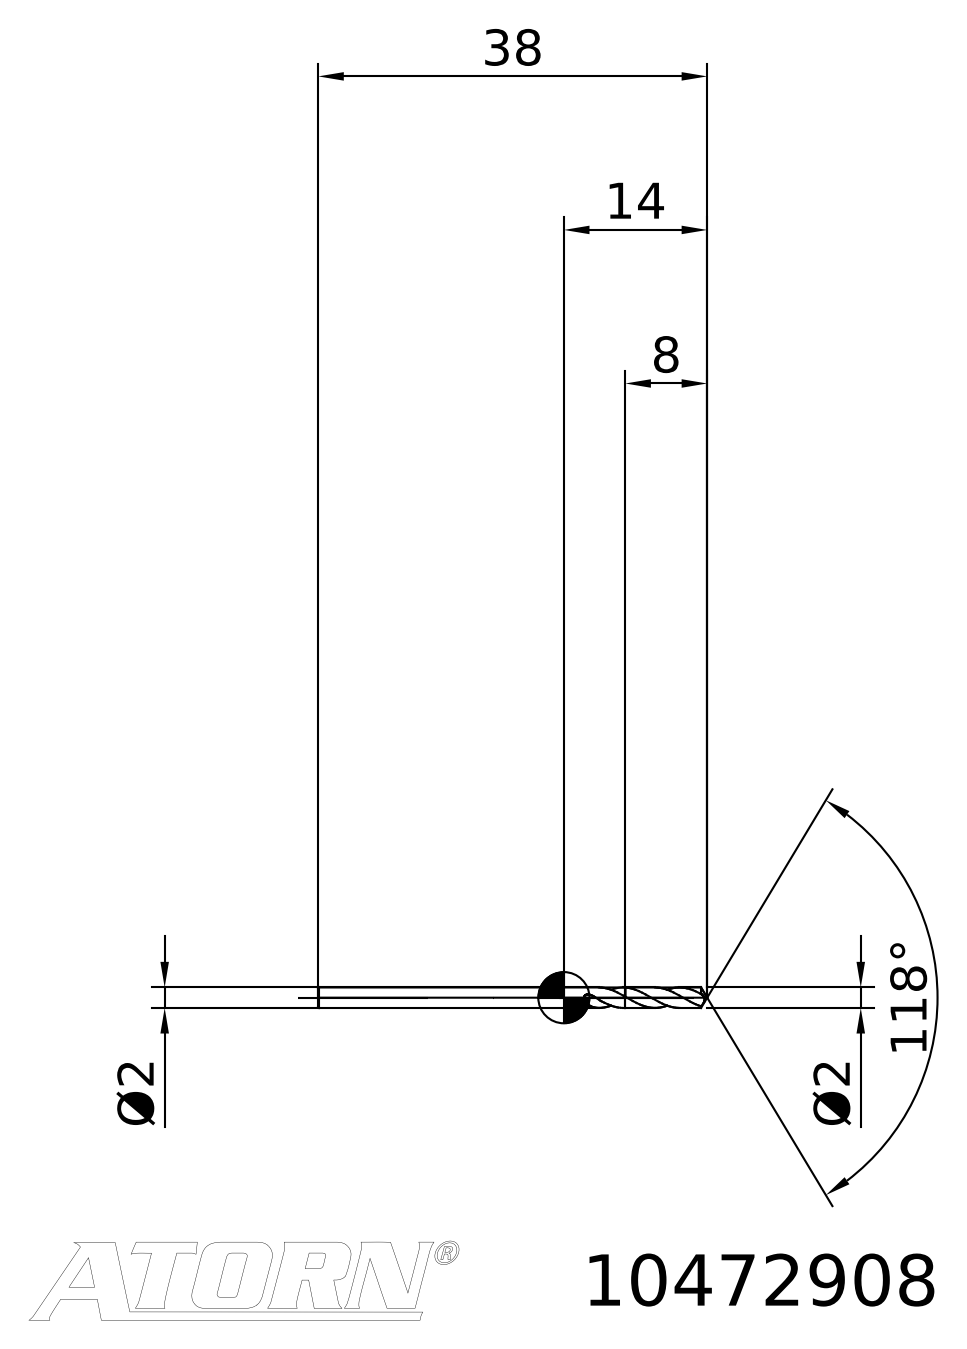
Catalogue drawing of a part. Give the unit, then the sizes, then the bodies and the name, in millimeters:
Units: millimetres
Overall size (bounding box): 38 × 4.36 × 3.02
Main face-to-face distances: 30
Volume: 106 mm³ · Surface area: 251 mm²
Bodies: 2 solids, 25 faces (3 planar, 0 cylindrical, 22 other)
STEP written by: TDM (AUTOMOTIVE_DESIGN)
